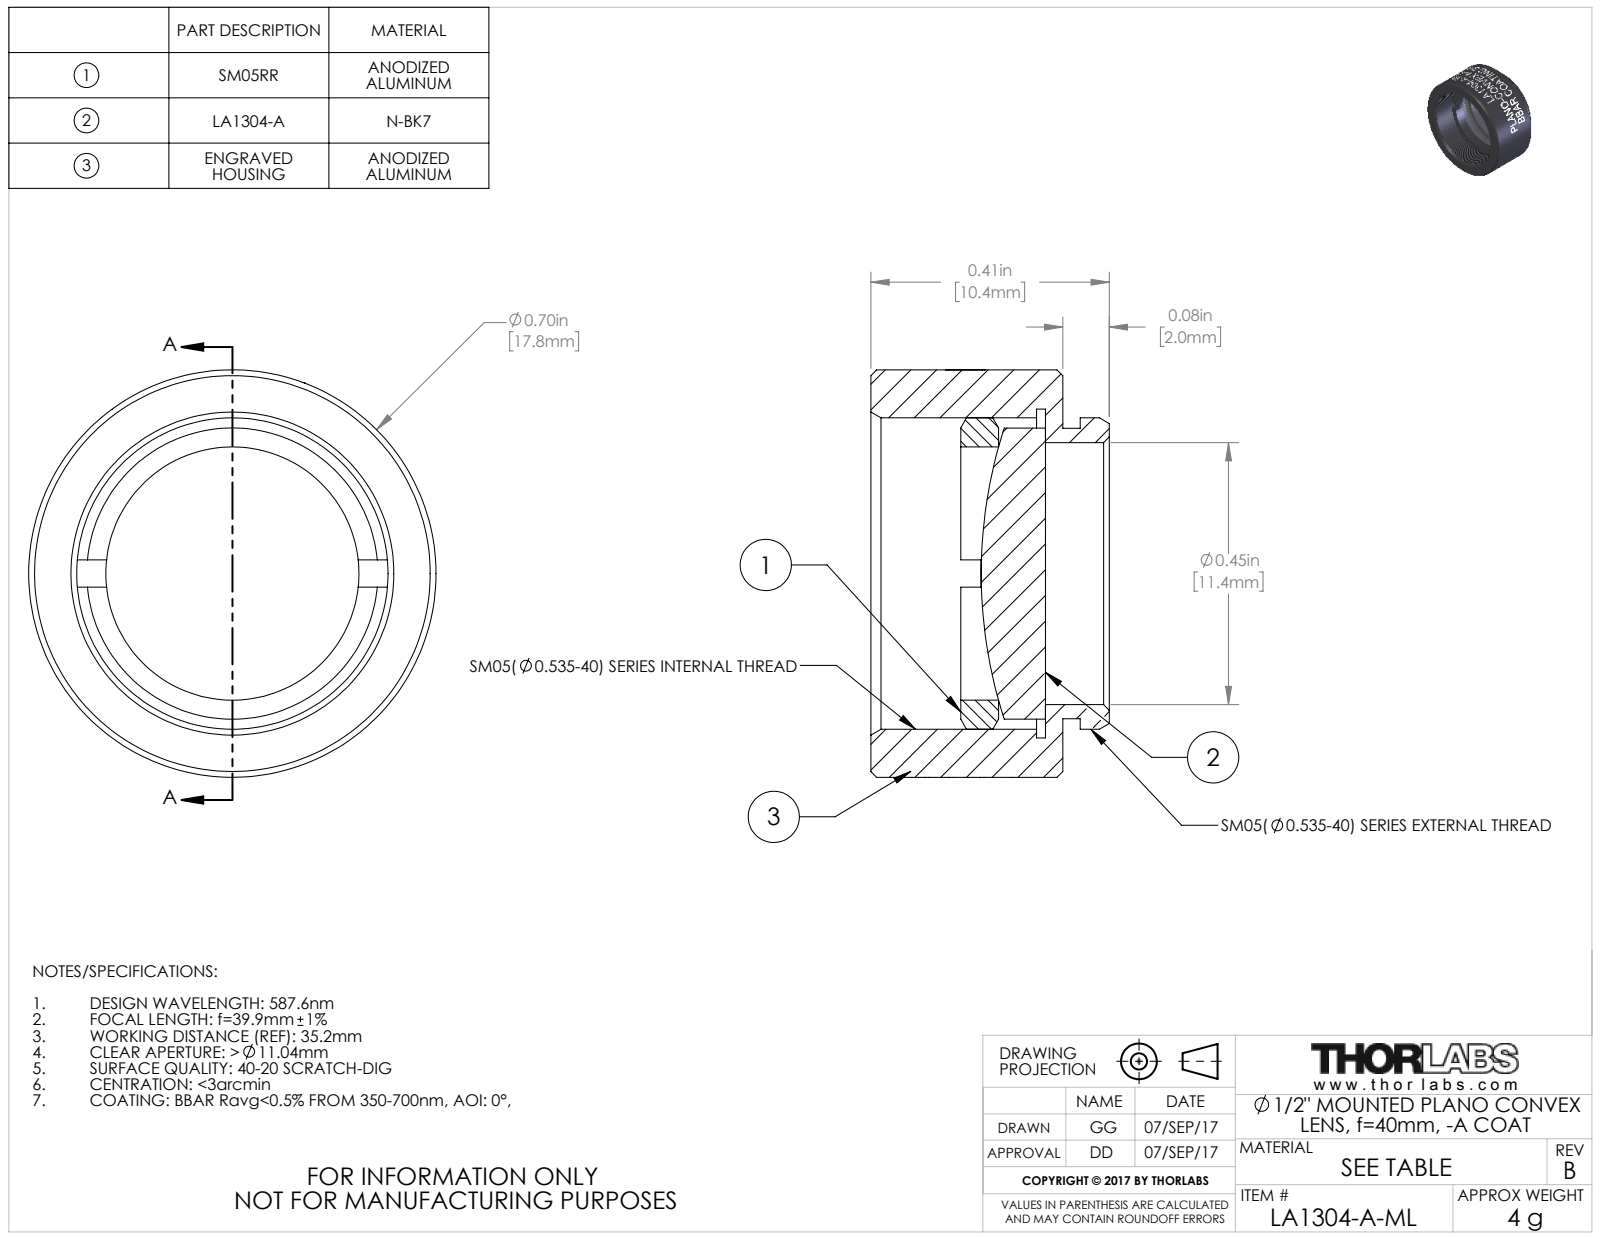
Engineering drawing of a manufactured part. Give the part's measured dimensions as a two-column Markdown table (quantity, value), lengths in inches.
| quantity | value |
| --- | --- |
| part name | 24407-E0W |
| STEP written by | SolidWorks 2016 (CONFIG_CONTROL_DESIGN) |
| units | inches |
| bodies | 3 solids, 277 faces (94 planar, 108 cylindrical, 75 other) |
| overall size | 0.7 × 0.7 × 0.41 |
| volume | 0.081 in³ |
| surface area | 2.856 in² |
| round holes (diameter × count) | 0.435 × 1, 0.45 × 1, 0.535 × 1, 0.565 × 1 |
| round bosses / shafts (diameter × count) | 0.7 × 1, 0.535 × 1, 0.5 × 1, 0.499 × 1 |
| partial cylindrical surfaces (radius × count) | 0.35 × 1 |
| main face-to-face distances | 0.03, 0.3, 0.33, 0.22, 0.111, 0.08, 0.176, 0.145, 0.065, 0.155 |
